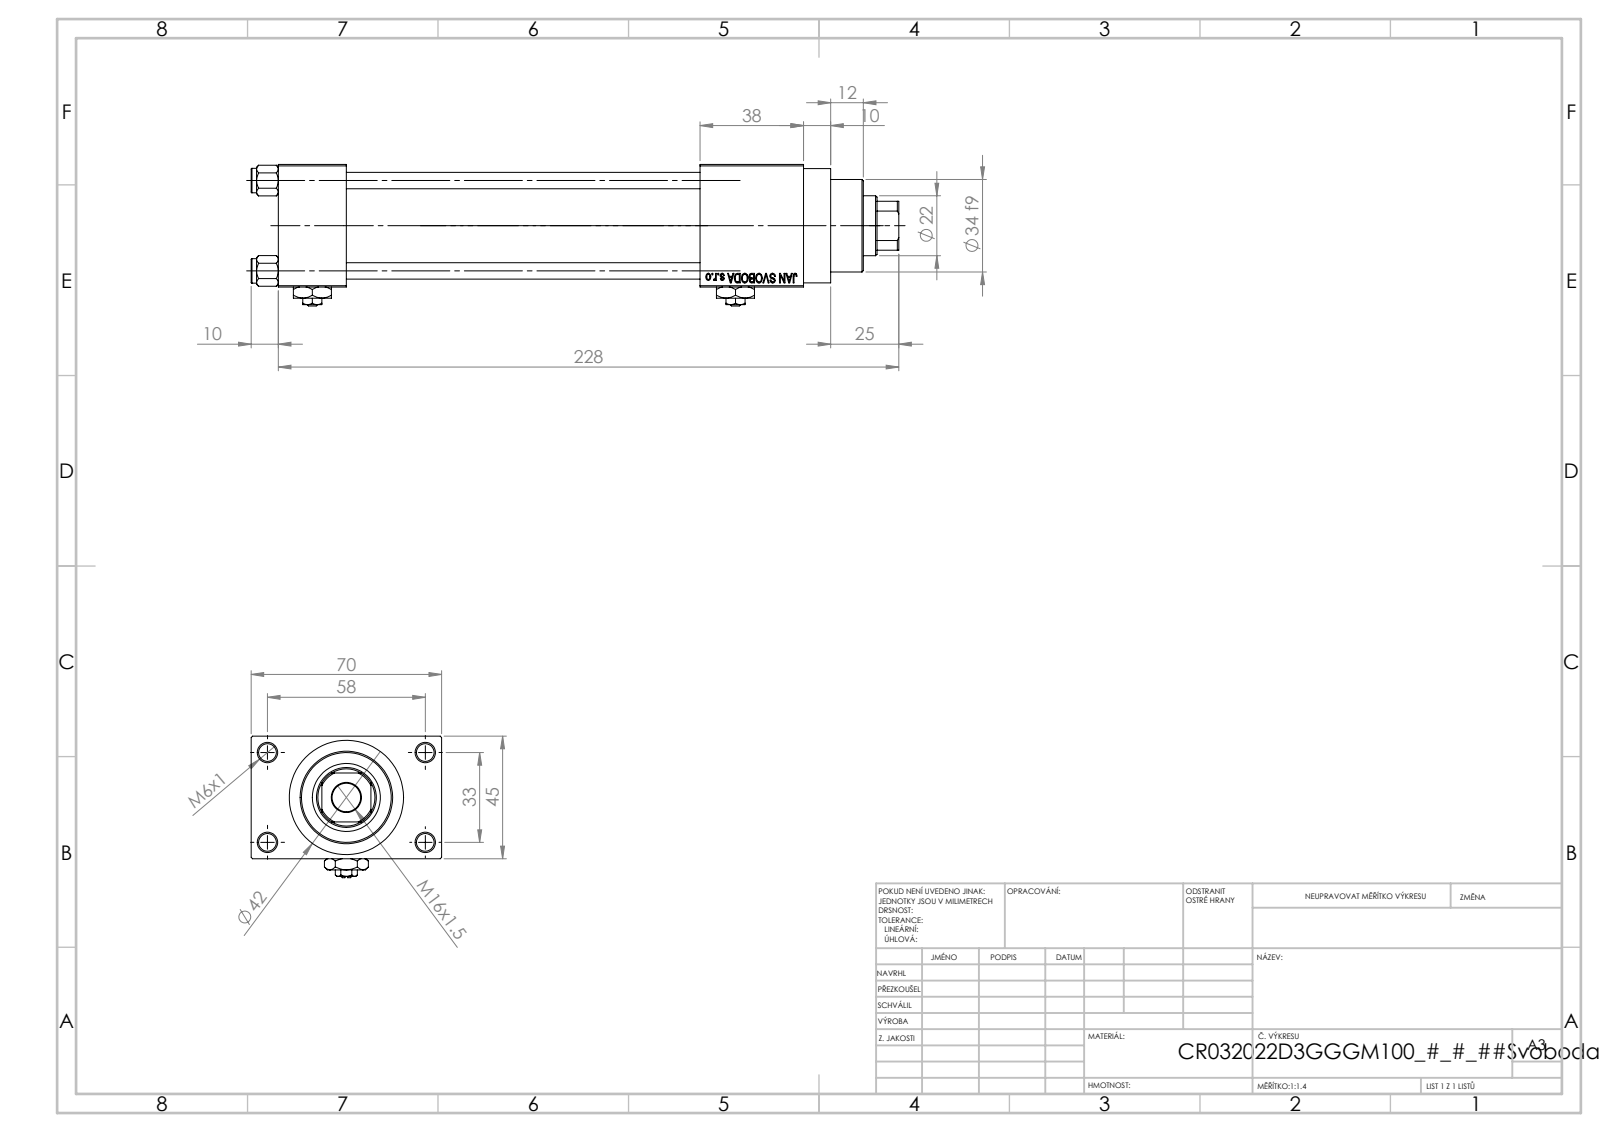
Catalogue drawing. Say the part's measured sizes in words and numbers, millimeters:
The part is named "V215_VC_A; V215CR_D_TYCINKA; Zatka_pro_OIL_PORT; NUT_M5_D (+2 more)". Its 3-D file was written by "SolidWorks 2019 (CONFIG_CONTROL_DESIGN)". It is 13 solids with 1202 faces: 542 planar, 100 cylindrical and 560 other. Overall it measures 238 by 70 by 52 millimeters. Its volume is 309 215 cubic millimeters and its surface area 110 354 square millimeters. Round holes: 4 of diameter 6, 4 of diameter 6.5, 2 of diameter 7, 2 of diameter 13.16, 2 of diameter 20, 1 of diameter 10.5, 1 of diameter 22, 1 of diameter 24, 1 of diameter 25, 1 of diameter 32, 1 of diameter 33. Round bosses or shafts: 4 of diameter 9, 1 of diameter 42, 1 of diameter 38, 1 of diameter 34. Partial cylindrical surfaces (rounded edges, fillets, slot ends): 1 of radius 10.5. The main face-to-face distances are 45, 25, 12.5, 57.5, 130, 155, 168, 38, 70, 193. The hole center spacings are 12.4, 23.48, 33.2, 33.37, 35.35, 45.6, 56.35, 33.
